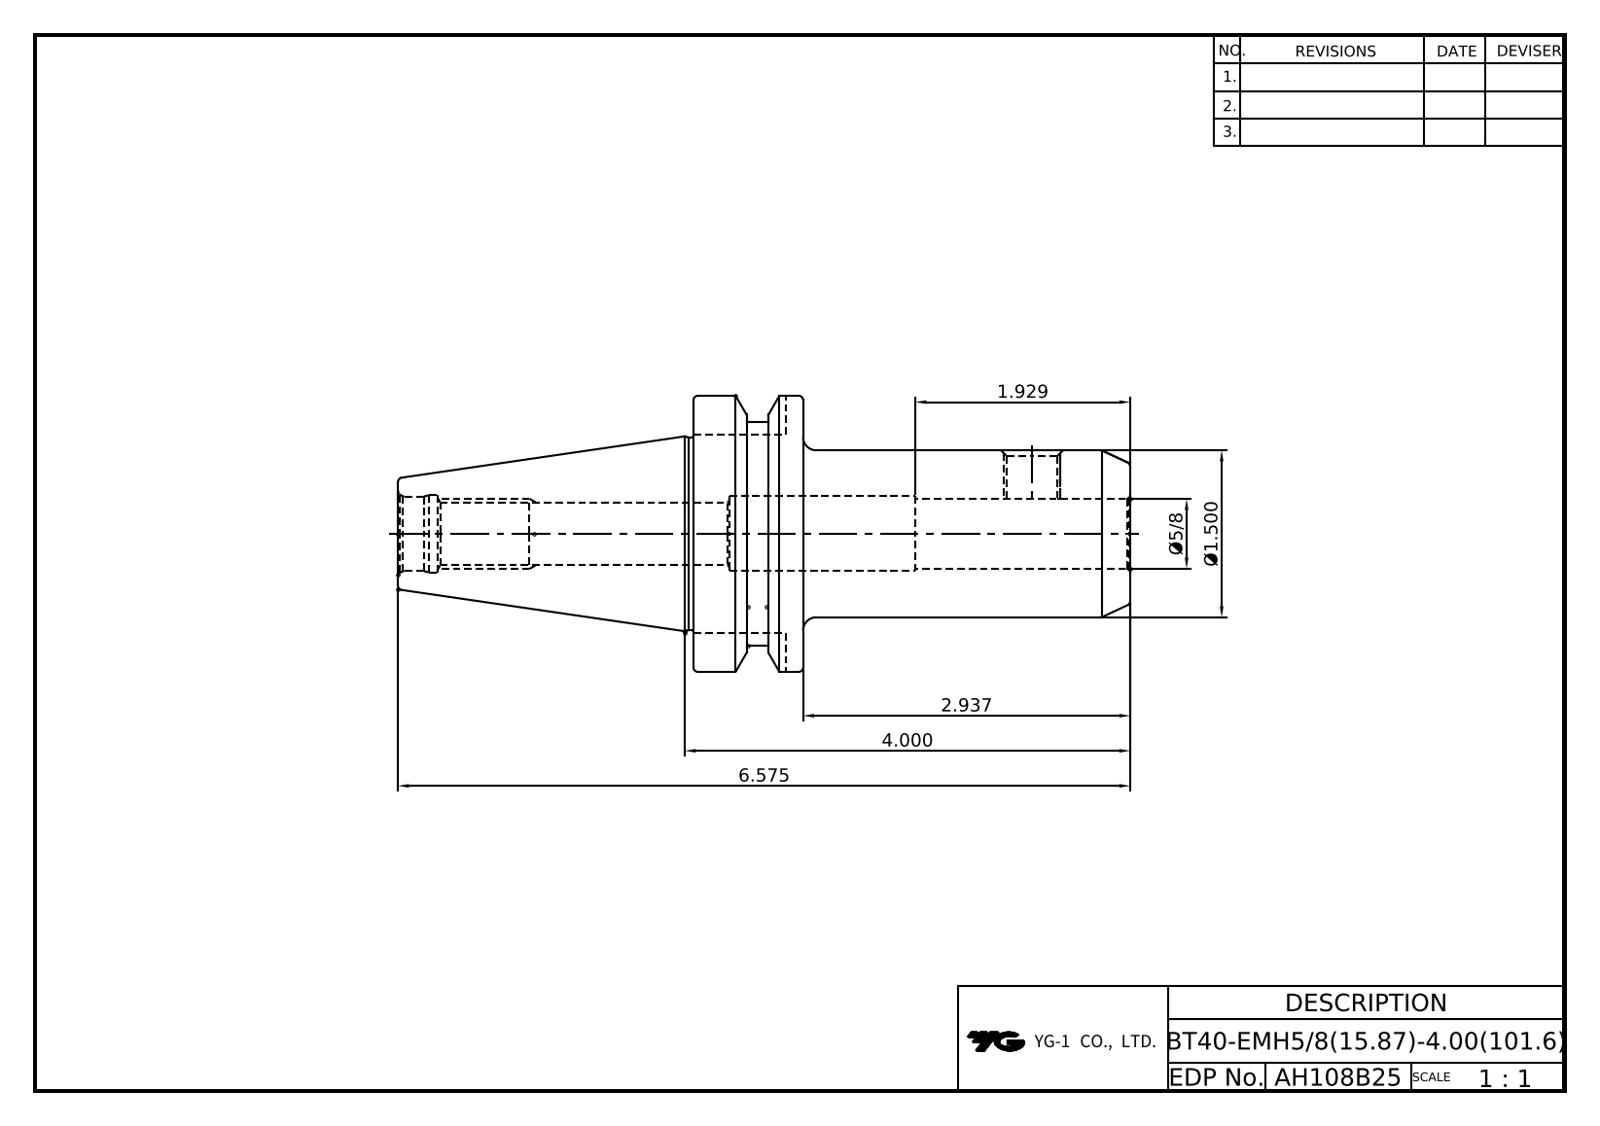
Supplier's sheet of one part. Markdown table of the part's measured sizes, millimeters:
| quantity | value |
| --- | --- |
| part name | LO-BT40-EMH15.875-101.6 |
| STEP written by | Autodesk Inventor 2022 (AUTOMOTIVE_DESIGN) |
| units | millimeters |
| bodies | 1 solid, 53 faces (17 planar, 16 cylindrical, 20 other) |
| overall size | 167 × 63 × 63 |
| volume | 185 758 mm³ |
| surface area | 35 110 mm² |
| round holes (diameter × count) | 11.33 × 1, 13.5 × 1, 13.84 × 1, 15.88 × 1, 17 × 1, 17.08 × 1, 17.6 × 1 |
| round bosses / shafts (diameter × count) | 63 × 1, 52.6 × 1, 44 × 1, 38.1 × 1 |
| partial cylindrical surfaces (radius × count) | 8.05 × 1 |
| main face-to-face distances | 25, 99.6, 74.6, 45.2, 16.1, 67.4, 92.4, 167, 84.5, 17.1 |
